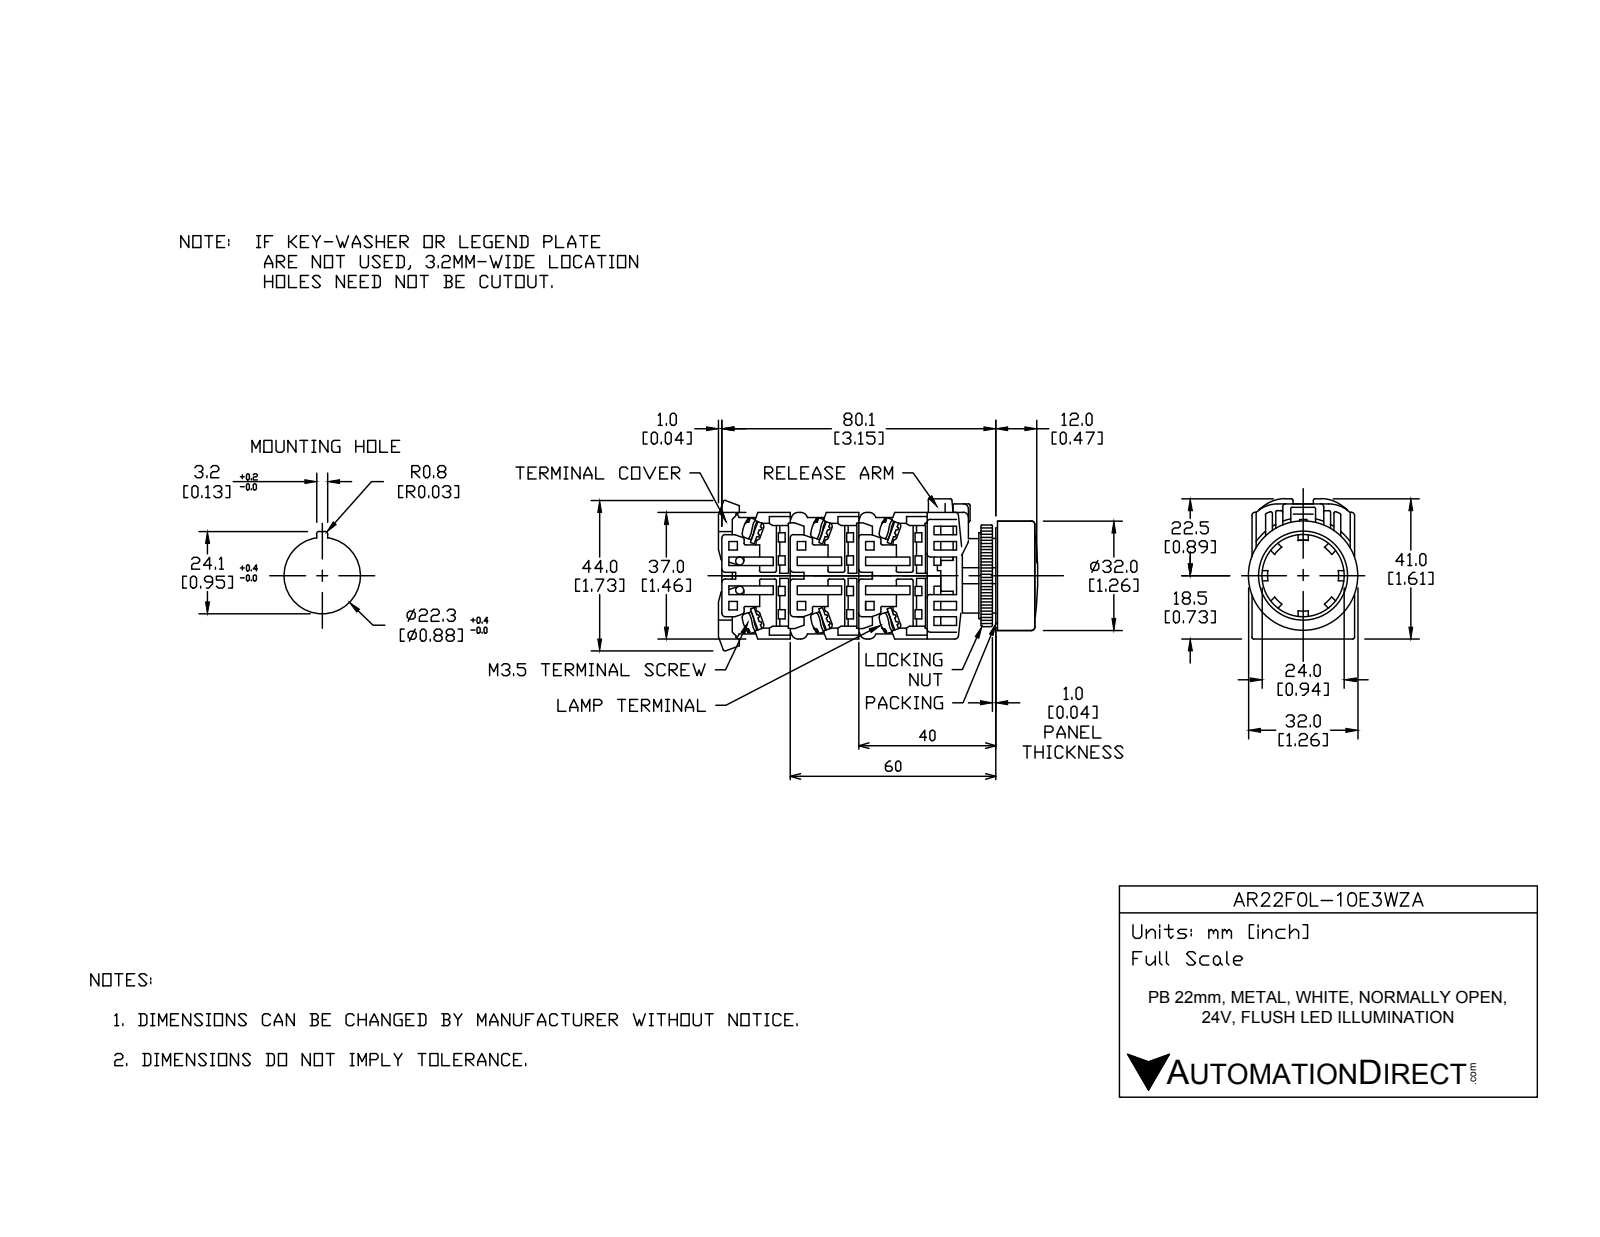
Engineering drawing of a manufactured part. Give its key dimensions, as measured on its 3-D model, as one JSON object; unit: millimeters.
{"part_name": "AR22F0L-10E3WZA", "step_written_by": "SolidWorks 2017 (AUTOMOTIVE_DESIGN)", "units": "millimeters", "bodies": {"solids": 18, "faces": 475, "planar": 329, "cylindrical": 111, "other": 35}, "overall_size": [52.75, 43.81, 32], "volume_mm3": 36367, "surface_area_mm2": 24064, "round_holes": [[21.8, 1], [22, 1], [25, 1], [31, 1]], "round_bosses_or_shafts": [[5, 4], [32, 1], [30.5, 1], [29.8, 1], [24, 1], [23.8, 1], [21.75, 1], [17, 1]], "partial_cylinders_radius": [[0.5, 39], [1.75, 8], [5, 4], [4, 2], [16.59, 1], [17.59, 1]], "face_to_face_distances": [1, 18, 28.5, 48.5, 20, 29, 3, 2, 21, 0.5]}
